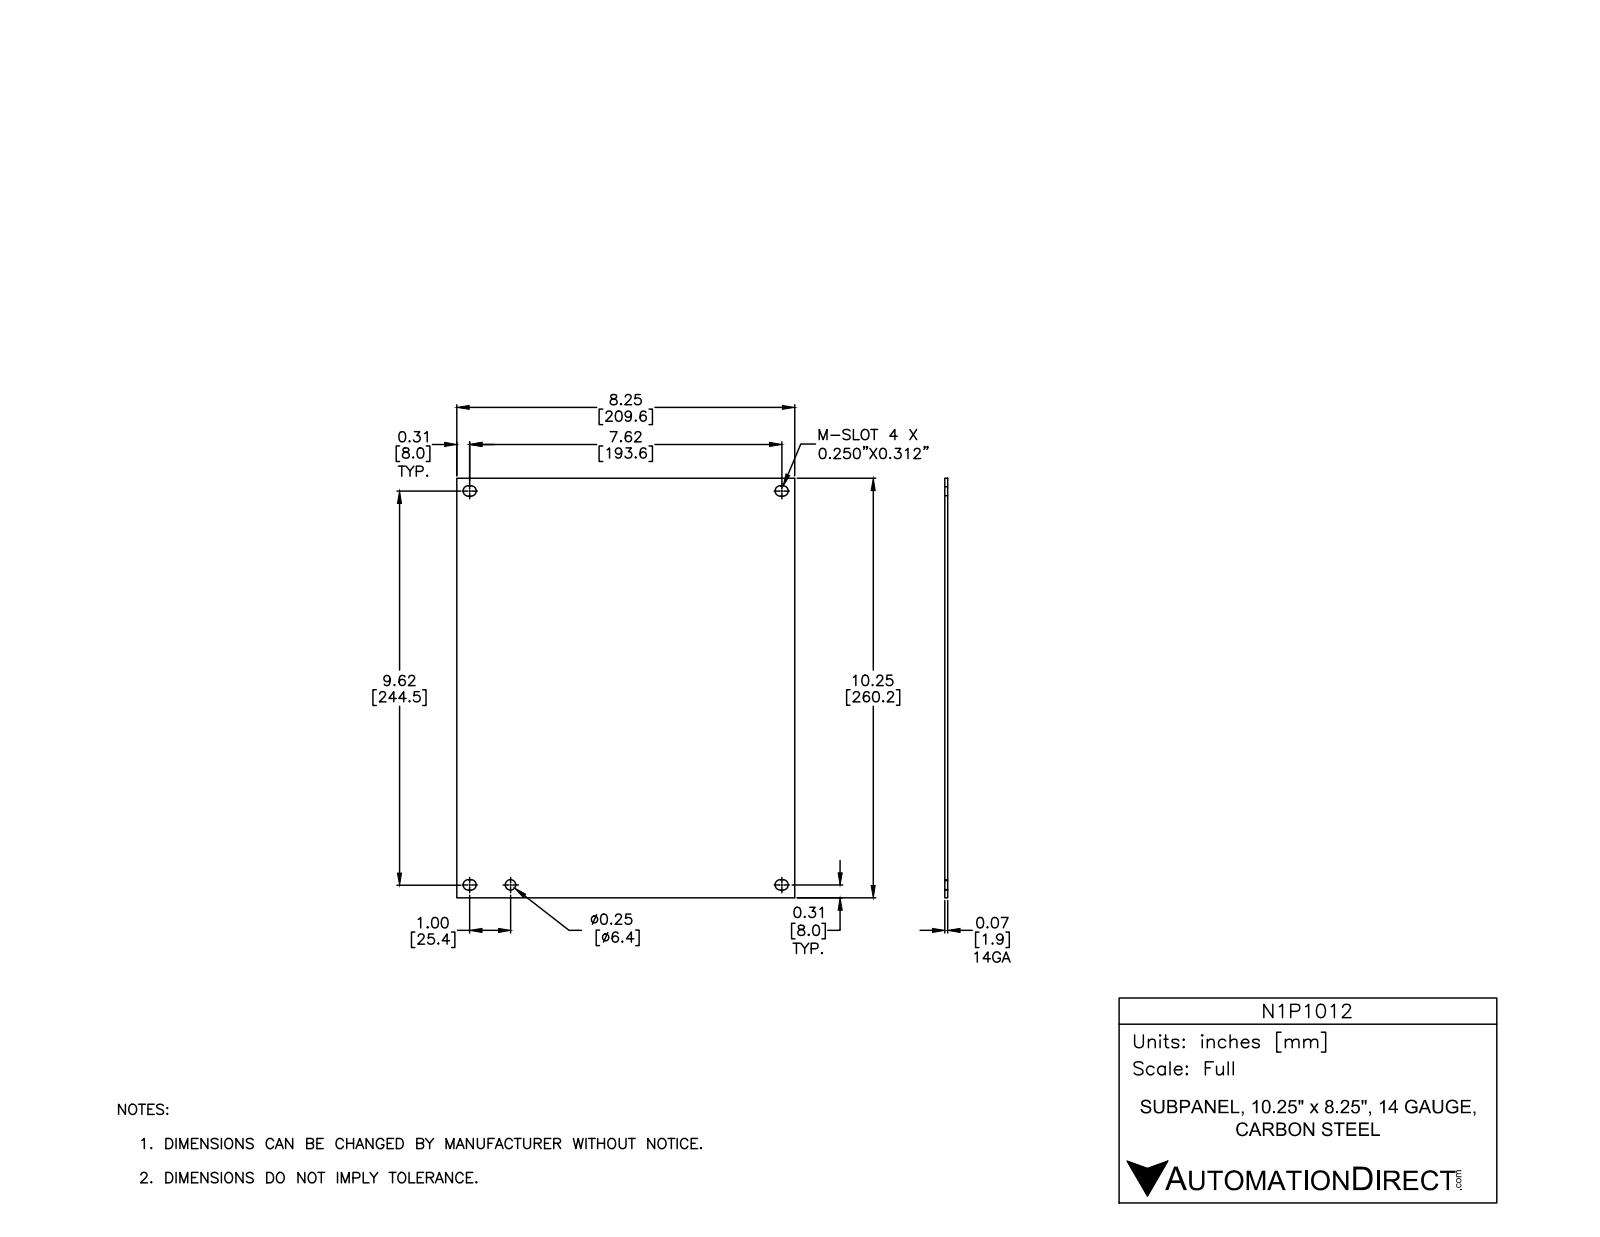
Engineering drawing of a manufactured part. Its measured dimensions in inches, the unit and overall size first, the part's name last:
Units: inches
Overall size (bounding box): 10.25 × 8.25 × 0.074
Round holes (diameter × count): ⌀0.25 ×1
Partial cylindrical surfaces — rounded edges, fillets, slot ends (radius × count): R0.125 ×8
Main face-to-face distances: 0.074, 8.25, 10.25, 0.188, 0.438, 9.812, 10.062, 9.624, 0.25, 9.874
Volume: 6.235 in³ · Surface area: 171.6 in²
Bodies: 1 solid, 23 faces (14 planar, 9 cylindrical, 0 other)
Part name (STEP PRODUCT): N1P1012
STEP written by: Autodesk Inventor 2012 (AUTOMOTIVE_DESIGN)
